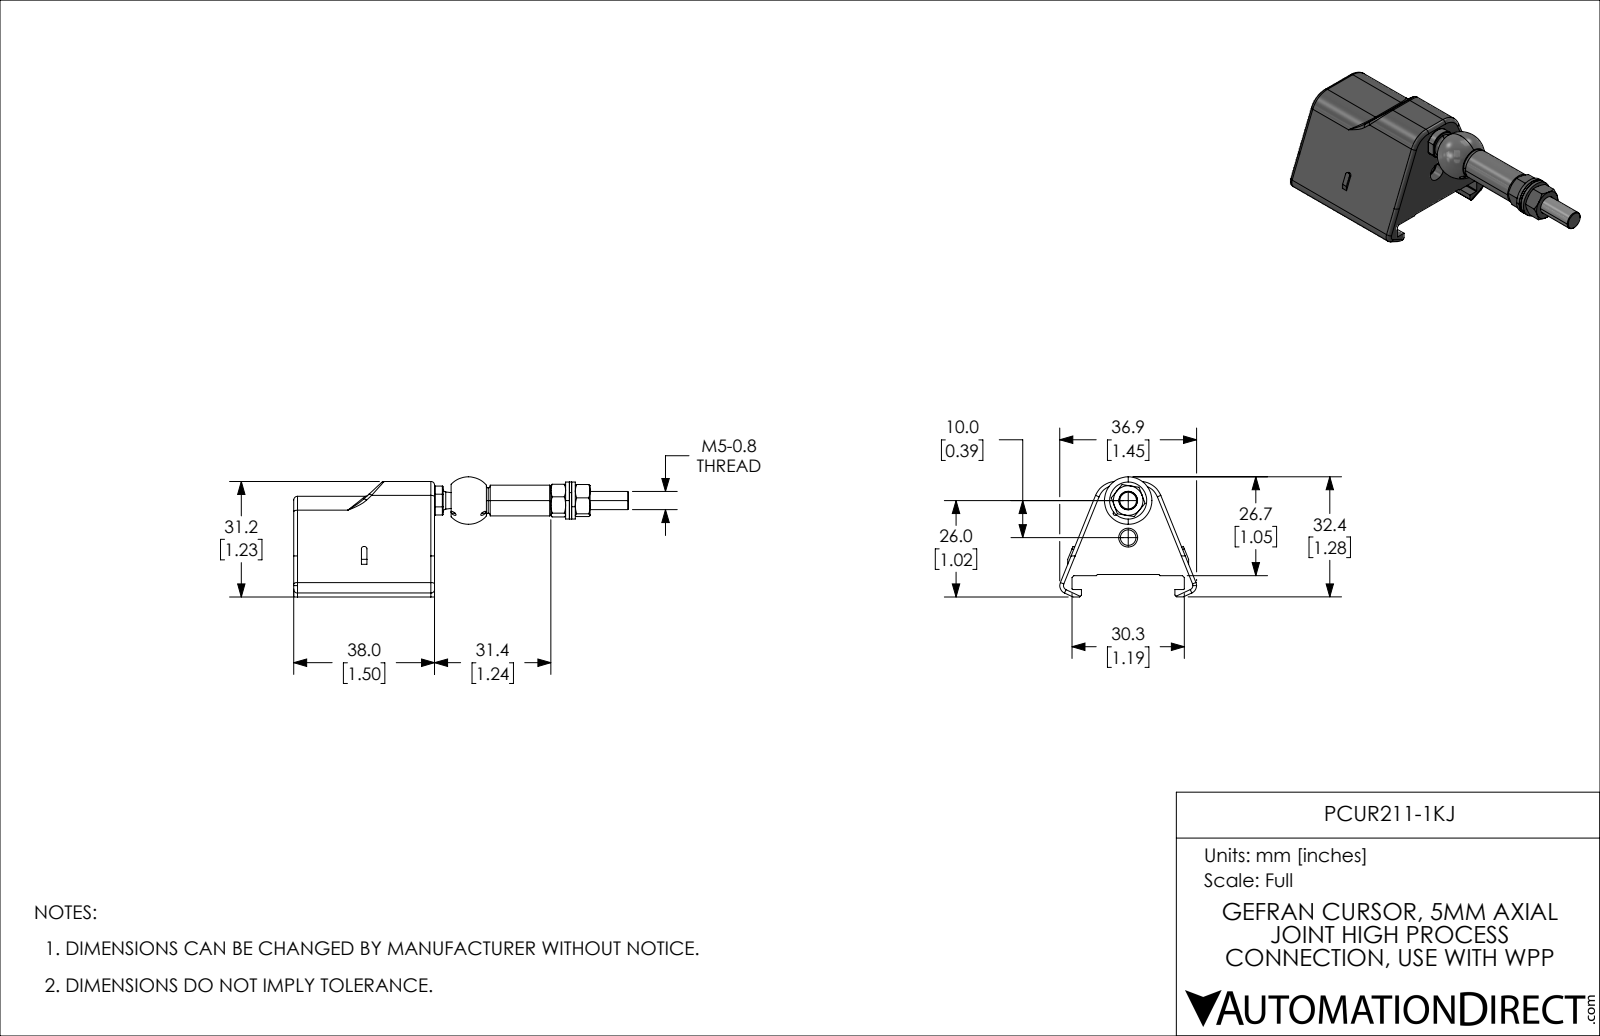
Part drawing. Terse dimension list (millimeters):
name: PCUR211-1KJ
written by: SolidWorks 2021 (CONFIG_CONTROL_DESIGN)
unit: mm
bodies: 9 solids, 274 faces (97 planar, 89 cylindrical, 88 other)
size: 90.34 × 36.91 × 32.4
volume: 24 787 mm³; area: 10 698 mm²
holes: 2× ⌀4.2, 2× ⌀5.1, 1× ⌀1.1, 1× ⌀5, 1× ⌀5.3
bosses: 1× ⌀10, 1× ⌀8.3, 1× ⌀4.89
rounds: 14× R1, 8× R0.45, 6× R0.2, 4× R0.7, 4× R6, 2× R2.2, 1× R3.9
face distances: 38, 12, 13, 25, 9.15, 21.15, 2, 5.75, 1, 6.6
hole spacings: 4.91, 7.43, 10
